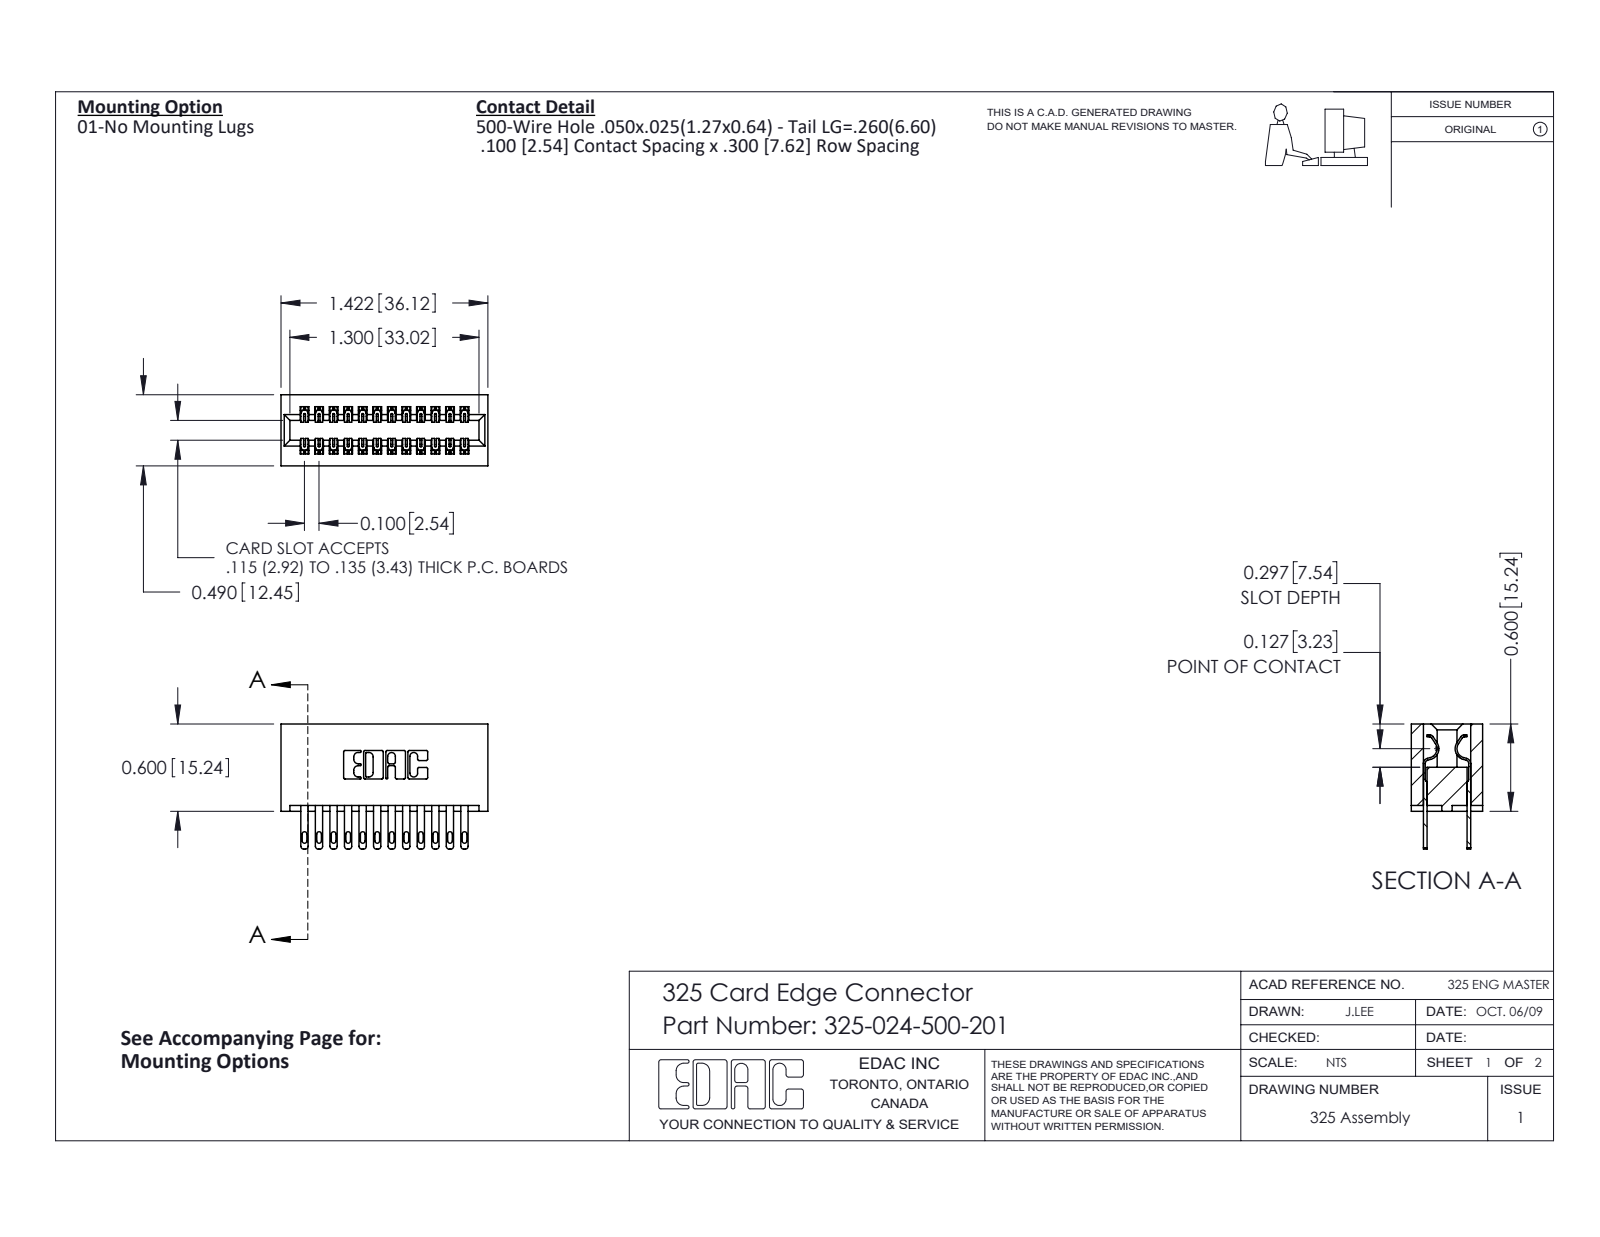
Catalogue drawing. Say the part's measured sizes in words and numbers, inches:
The part is named "325-292-001_325-293-100; 325-024-500-201; 325 Part_Lugless". Its 3-D file was written by "SolidWorks 2016 (CONFIG_CONTROL_DESIGN)". It is 25 solids with 1258 faces: 786 planar, 472 cylindrical and 0 other. Overall it measures 1.422 by 0.86 by 0.49 inches. Its volume is 0.31 cubic inches and its surface area 9.828 square inches. Partial cylindrical surfaces (rounded edges, fillets, slot ends): 36 of radius 0.006, 24 of radius 0.016, 24 of radius 0.02, 22 of radius 0.01, 6 of radius 0.007, 6 of radius 0.031, 3 of radius 0.026, 2 of radius 0.014. The main face-to-face distances are 0.3, 0.083, 0.407, 0.1, 0.107, 0.383, 0.025, 0.2, 0.49, 0.325.
